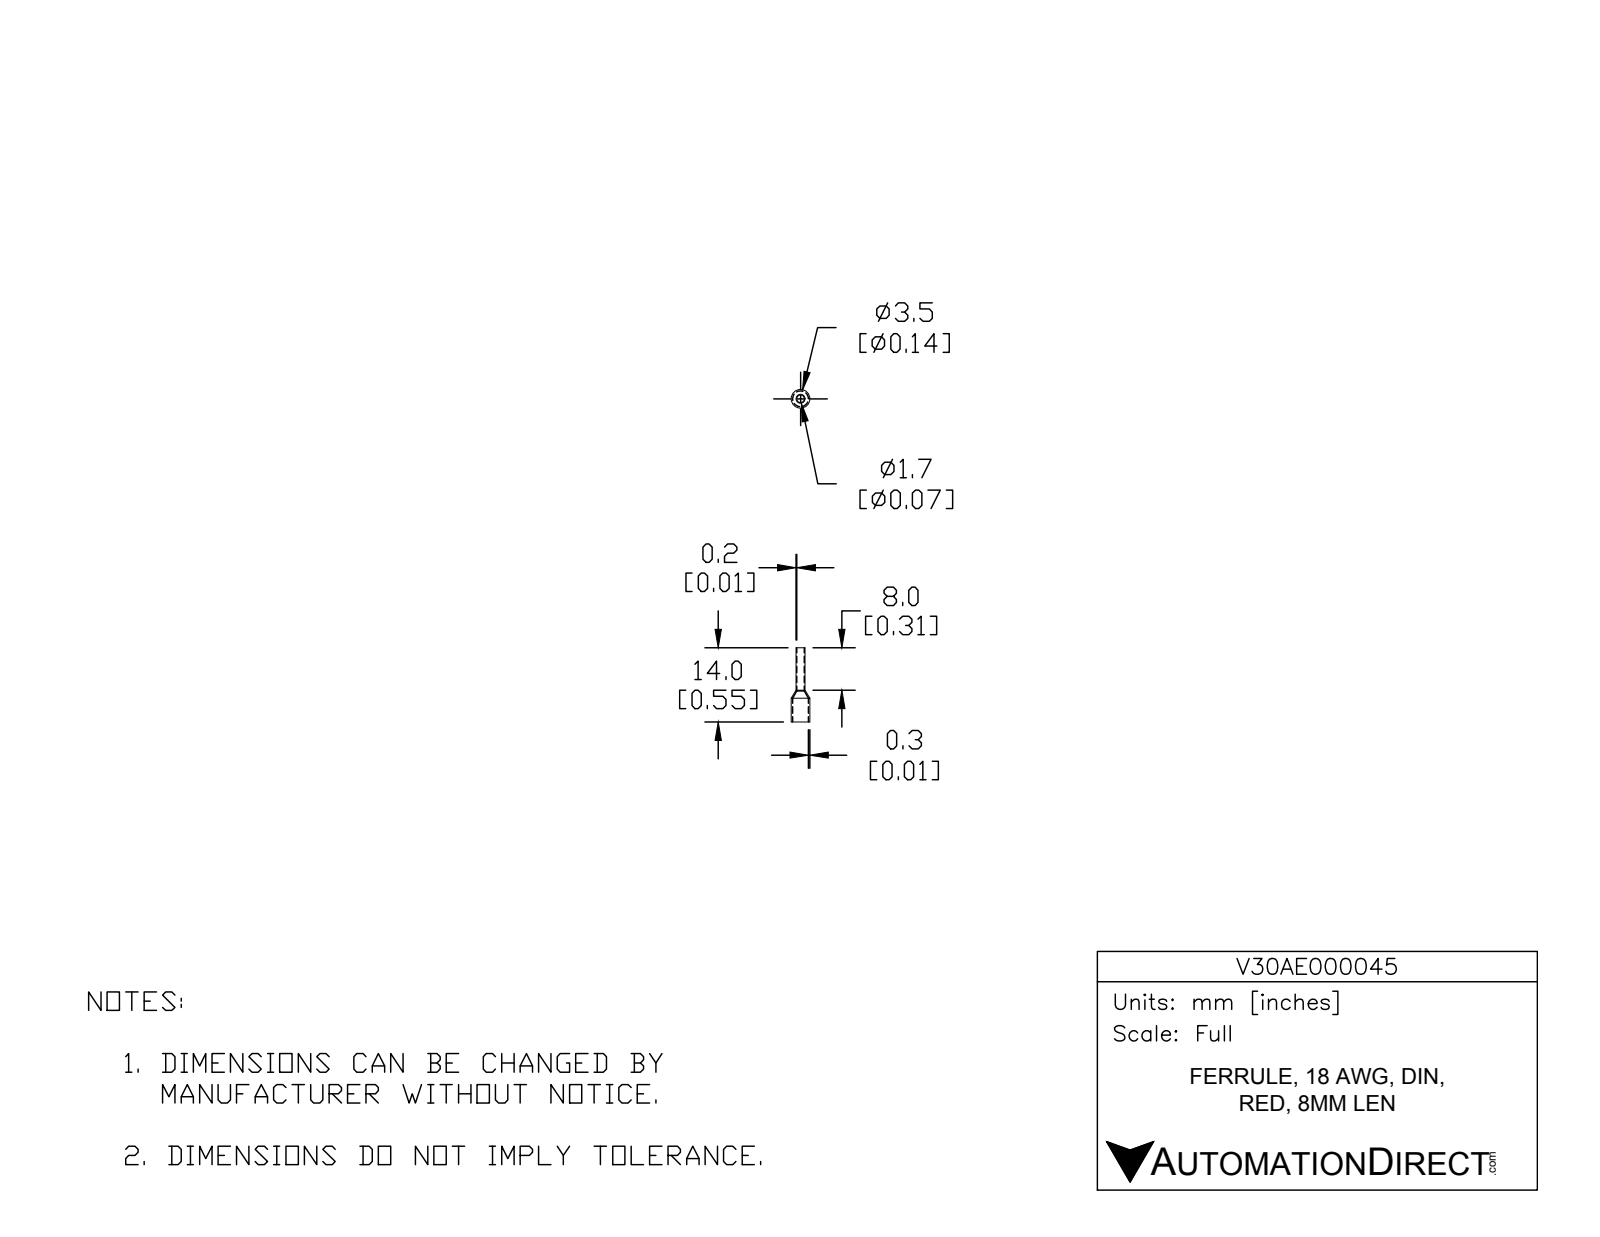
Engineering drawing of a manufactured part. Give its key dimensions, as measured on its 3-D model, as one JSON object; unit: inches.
{"part_name": "V30AE000045", "step_written_by": "SolidWorks 2017 (AUTOMOTIVE_DESIGN)", "units": "inches", "bodies": {"solids": 1, "faces": 14, "planar": 2, "cylindrical": 8, "other": 4}, "overall_size": [0.551, 0.138, 0.138], "volume_in3": 0.001, "surface_area_in2": 0.308, "round_holes": [[0.055, 1], [0.118, 1]], "round_bosses_or_shafts": [[0.138, 1], [0.067, 1]], "face_to_face_distances": [0.551]}
